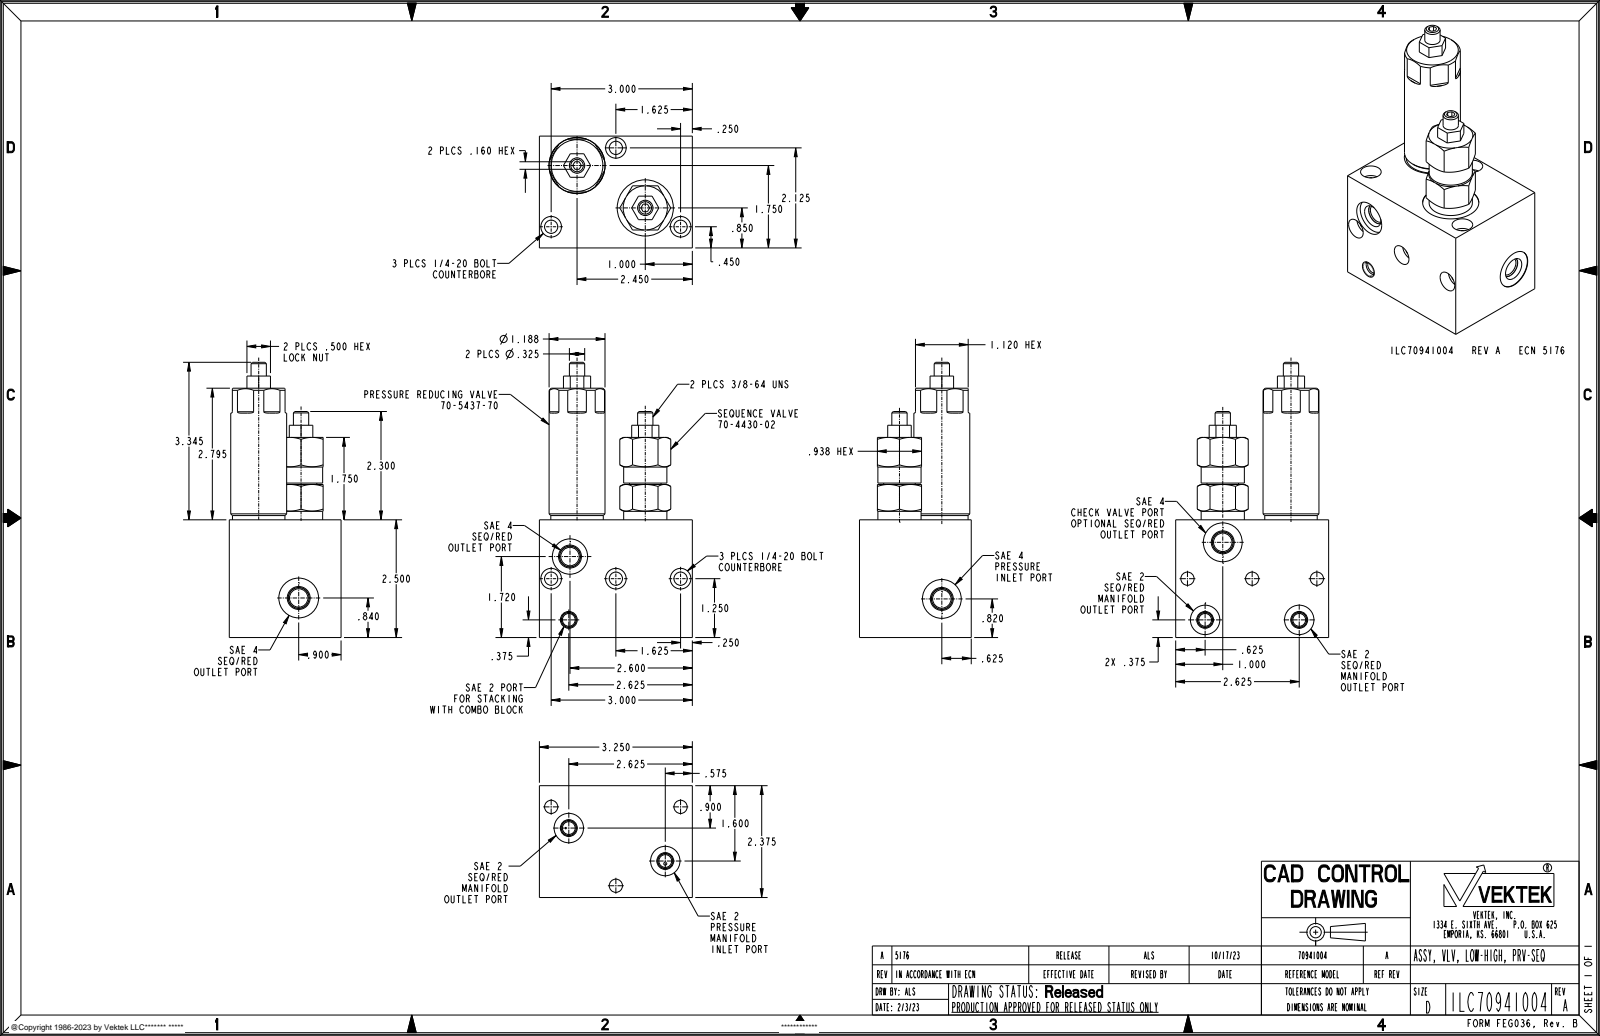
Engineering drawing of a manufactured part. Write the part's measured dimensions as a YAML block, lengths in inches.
part_name: "ILC70941004"
step_written_by: "CREO PARAMETRIC BY PTC INC, 2021164 (AUTOMOTIVE_DESIGN)"
units: inches
bodies: {solids: 1, faces: 275, planar: 93, cylindrical: 112, other: 70}
overall_size: [5.845, 3.25, 2.375]
volume: 21.96
surface_area: 84.89
round_holes:
  - {diameter: 0.281, count: 6}
  - {diameter: 0.438, count: 6}
  - {diameter: 0.272, count: 4}
  - {diameter: 0.392, count: 4}
  - {diameter: 0.625, count: 4}
  - {diameter: 0.825, count: 2}
  - {diameter: 1.193, count: 2}
  - {diameter: 0.75, count: 1}
  - {diameter: 0.845, count: 1}
round_bosses_or_shafts:
  - {diameter: 0.437, count: 4}
  - {diameter: 0.313, count: 4}
  - {diameter: 0.325, count: 2}
  - {diameter: 1.188, count: 1}
  - {diameter: 1.115, count: 1}
  - {diameter: 0.918, count: 1}
  - {diameter: 0.67, count: 1}
  - {diameter: 0.313, count: 1}
partial_cylinders:
  - {radius: 0.03, count: 6}
face_to_face_distances: [2.375, 3.25, 2.5, 0.938, 0.105, 2.27, 5.295, 2.795, 3.24, 0.105]
hole_center_spacings: [0.952, 1.329, 2.167, 2.531, 2.75, 0.586, 0.617, 0.85]
